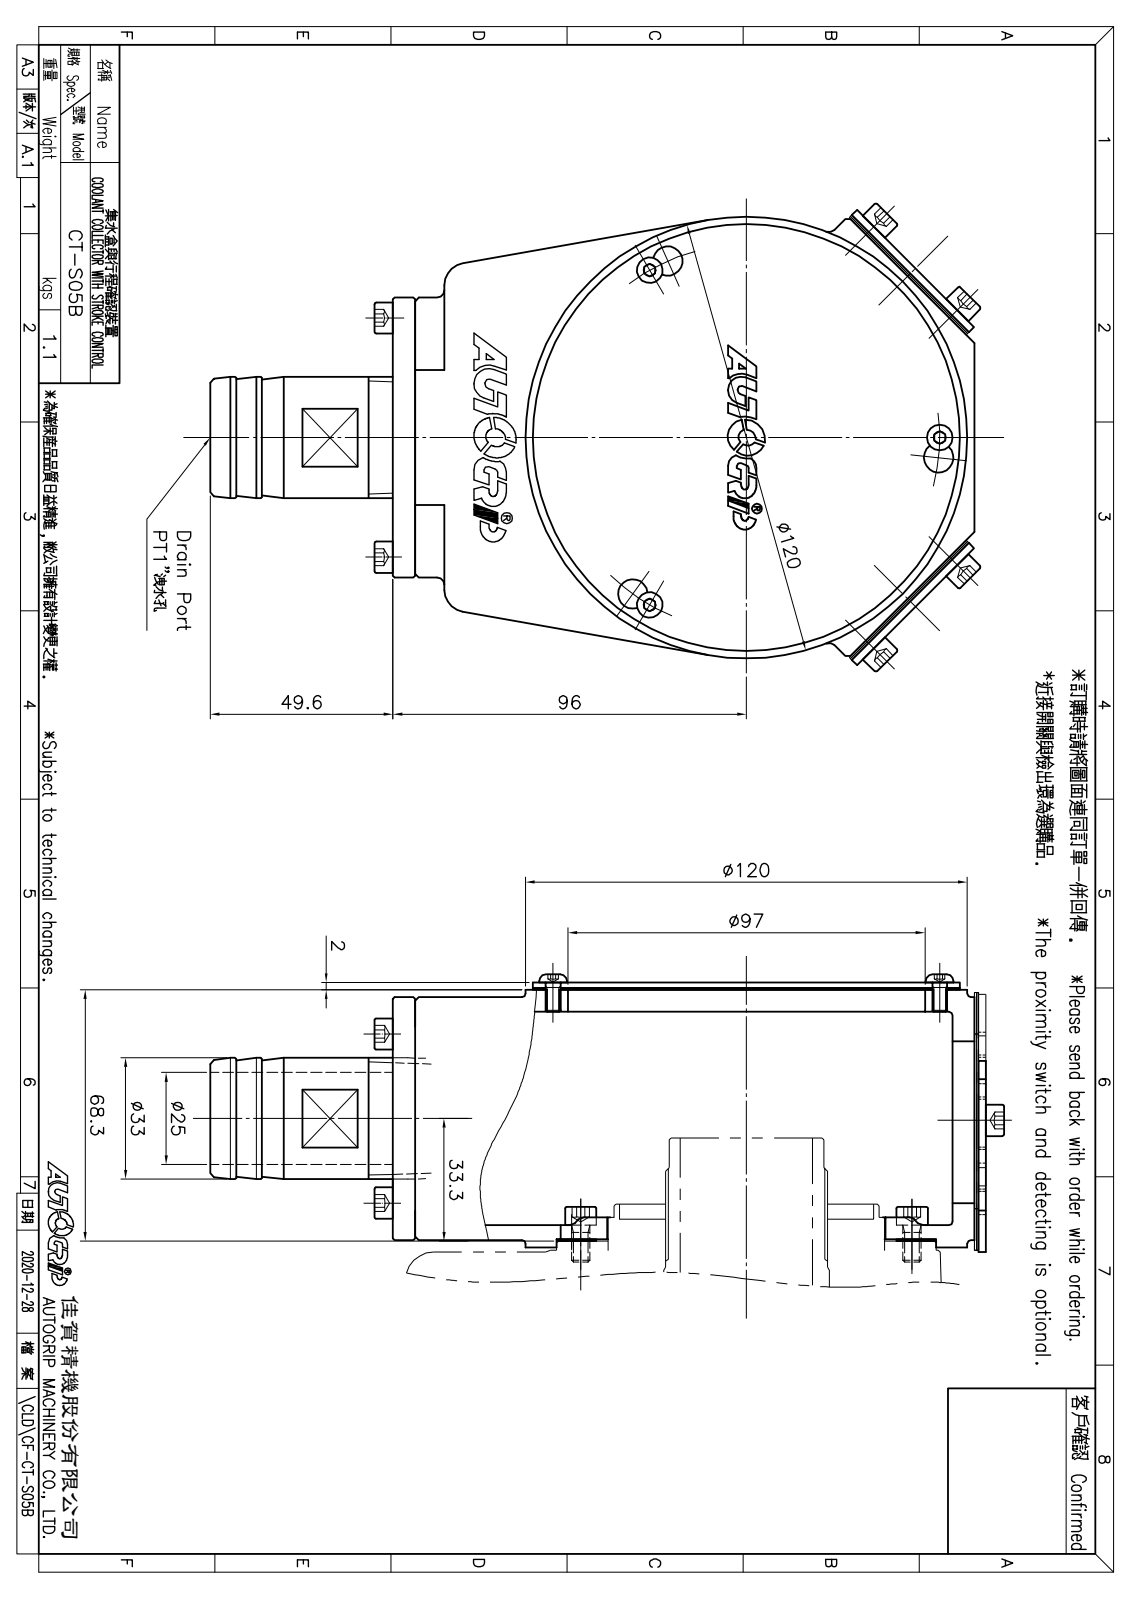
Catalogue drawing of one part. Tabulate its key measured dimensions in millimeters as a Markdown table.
| quantity | value |
| --- | --- |
| part name | CT-S08-11000; CT-S05-04000; CT-S08-08000; CT-S08-05000 (+8 more) |
| STEP written by | SolidWorks 2016 (CONFIG_CONTROL_DESIGN) |
| units | millimeters |
| bodies | 28 solids, 874 faces (481 planar, 209 cylindrical, 184 other) |
| overall size | 209.42 × 127.63 × 78.2 |
| volume | 308 742 mm³ |
| surface area | 188 375 mm² |
| round holes (diameter × count) | 4.1 × 8, 3.3 × 3, 5 × 3, 10.8 × 2, 5.5 × 1, 25 × 1, 50 × 1, 75.5 × 1, 97 × 1, 103 × 1 |
| round bosses / shafts (diameter × count) | 8.5 × 8, 5 × 8, 10 × 4, 6 × 4, 7.6 × 3, 4 × 3, 120 × 1, 116 × 1 |
| partial cylindrical surfaces (radius × count) | 2 × 16, 2.75 × 16, 7 × 8, 1.01 × 3, 4.05 × 2, 6 × 2, 1.35 × 1, 3.38 × 1 |
| main face-to-face distances | 0.5, 1, 1.5, 2, 6, 66, 4, 64, 64.5, 4.01 |
| hole center spacings | 32.5, 45.96, 52.5, 18.57, 21.05, 32, 65, 90.93 |
